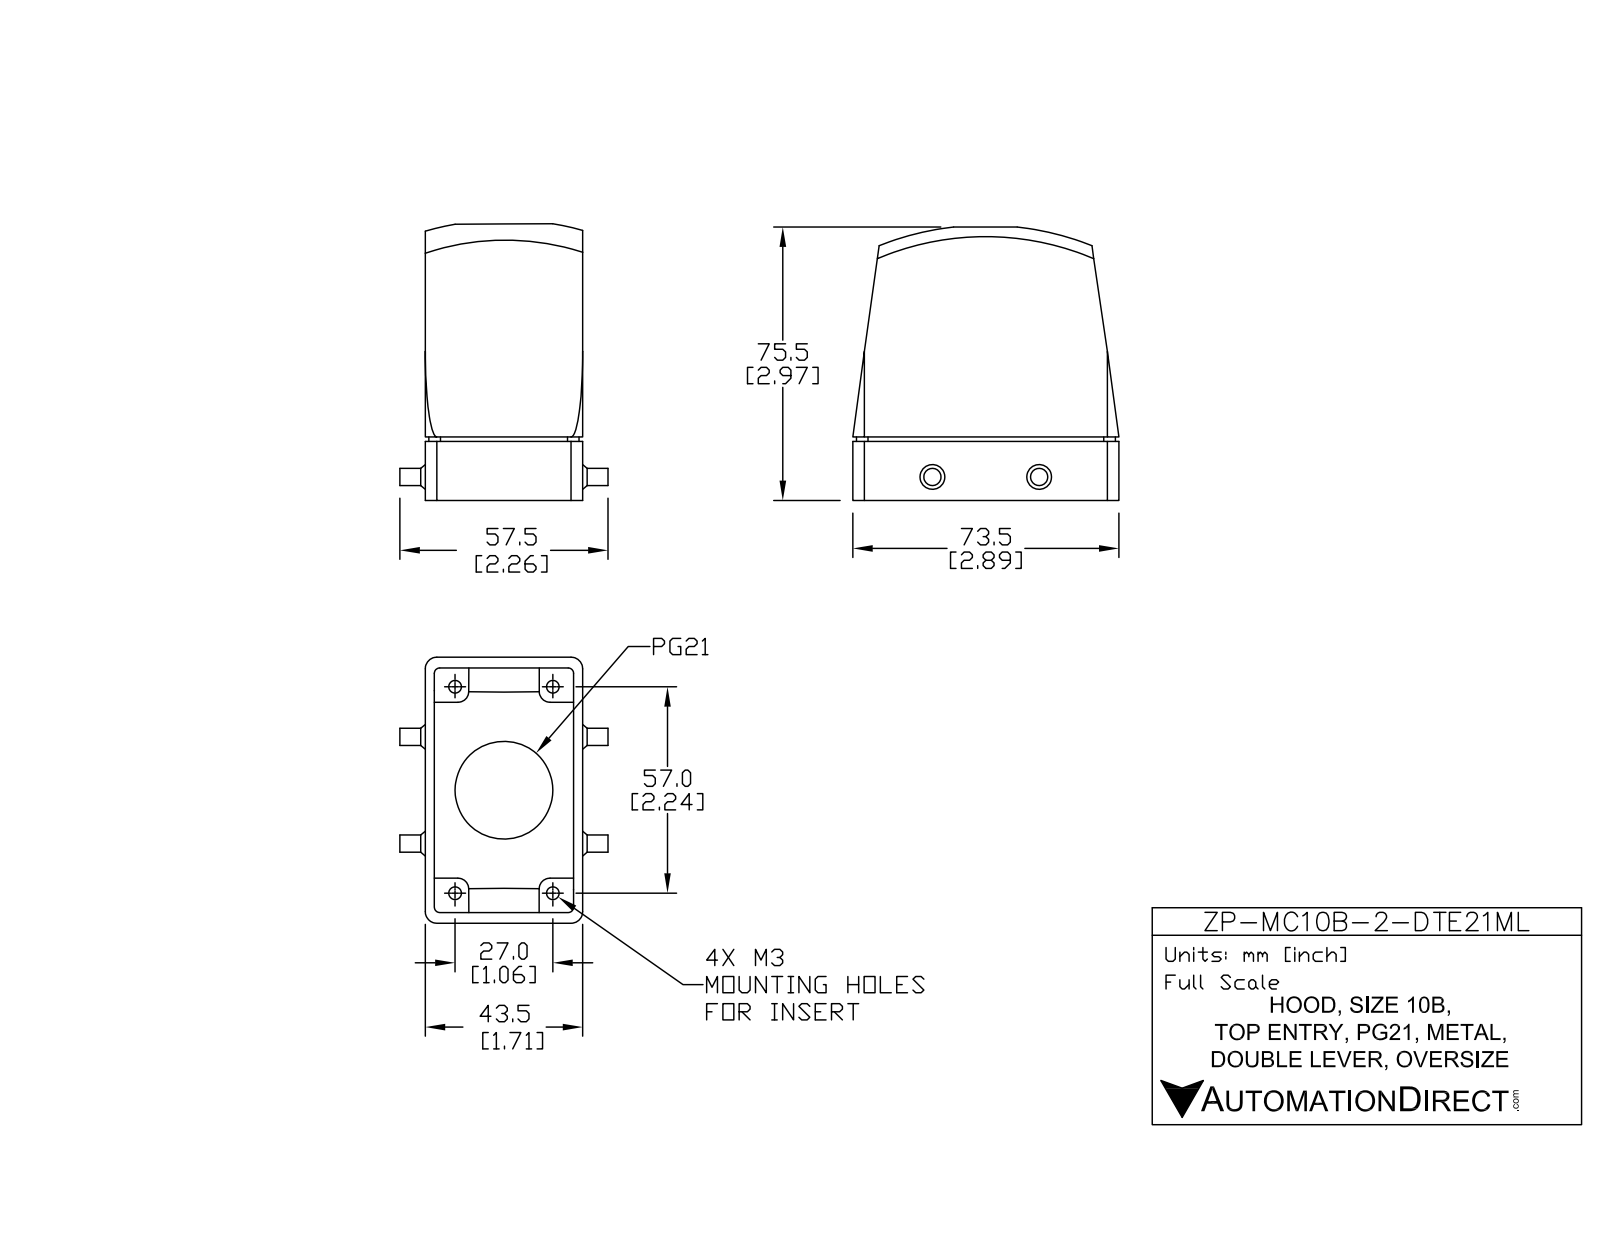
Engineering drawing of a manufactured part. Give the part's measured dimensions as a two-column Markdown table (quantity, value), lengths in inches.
| quantity | value |
| --- | --- |
| part name | ZP-MC10B-2-DTE21ML |
| STEP written by | SolidWorks 2021 (CONFIG_CONTROL_DESIGN) |
| units | inches |
| bodies | 1 solid, 488 faces (116 planar, 106 cylindrical, 266 other) |
| overall size | 3.15 × 2.894 × 2.26 |
| volume | 4.126 in³ |
| surface area | 57.74 in² |
| round holes (diameter × count) | 0.098 × 4, 0.138 × 4, 1.114 × 1 |
| round bosses / shafts (diameter × count) | 0.236 × 2, 0.193 × 2 |
| partial cylindrical surfaces (radius × count) | 0.024 × 8, 0.047 × 8, 0.059 × 8, 0.079 × 6, 0.039 × 4, 0.098 × 4, 0.154 × 4, 0.197 × 4 |
| main face-to-face distances | 0.114, 1.705, 1.707, 0.316, 1.709, 0.051, 0.053, 1.758, 1.76, 0.318 |
| hole center spacings | 1.242, 1.063, 2.244, 2.483 |
